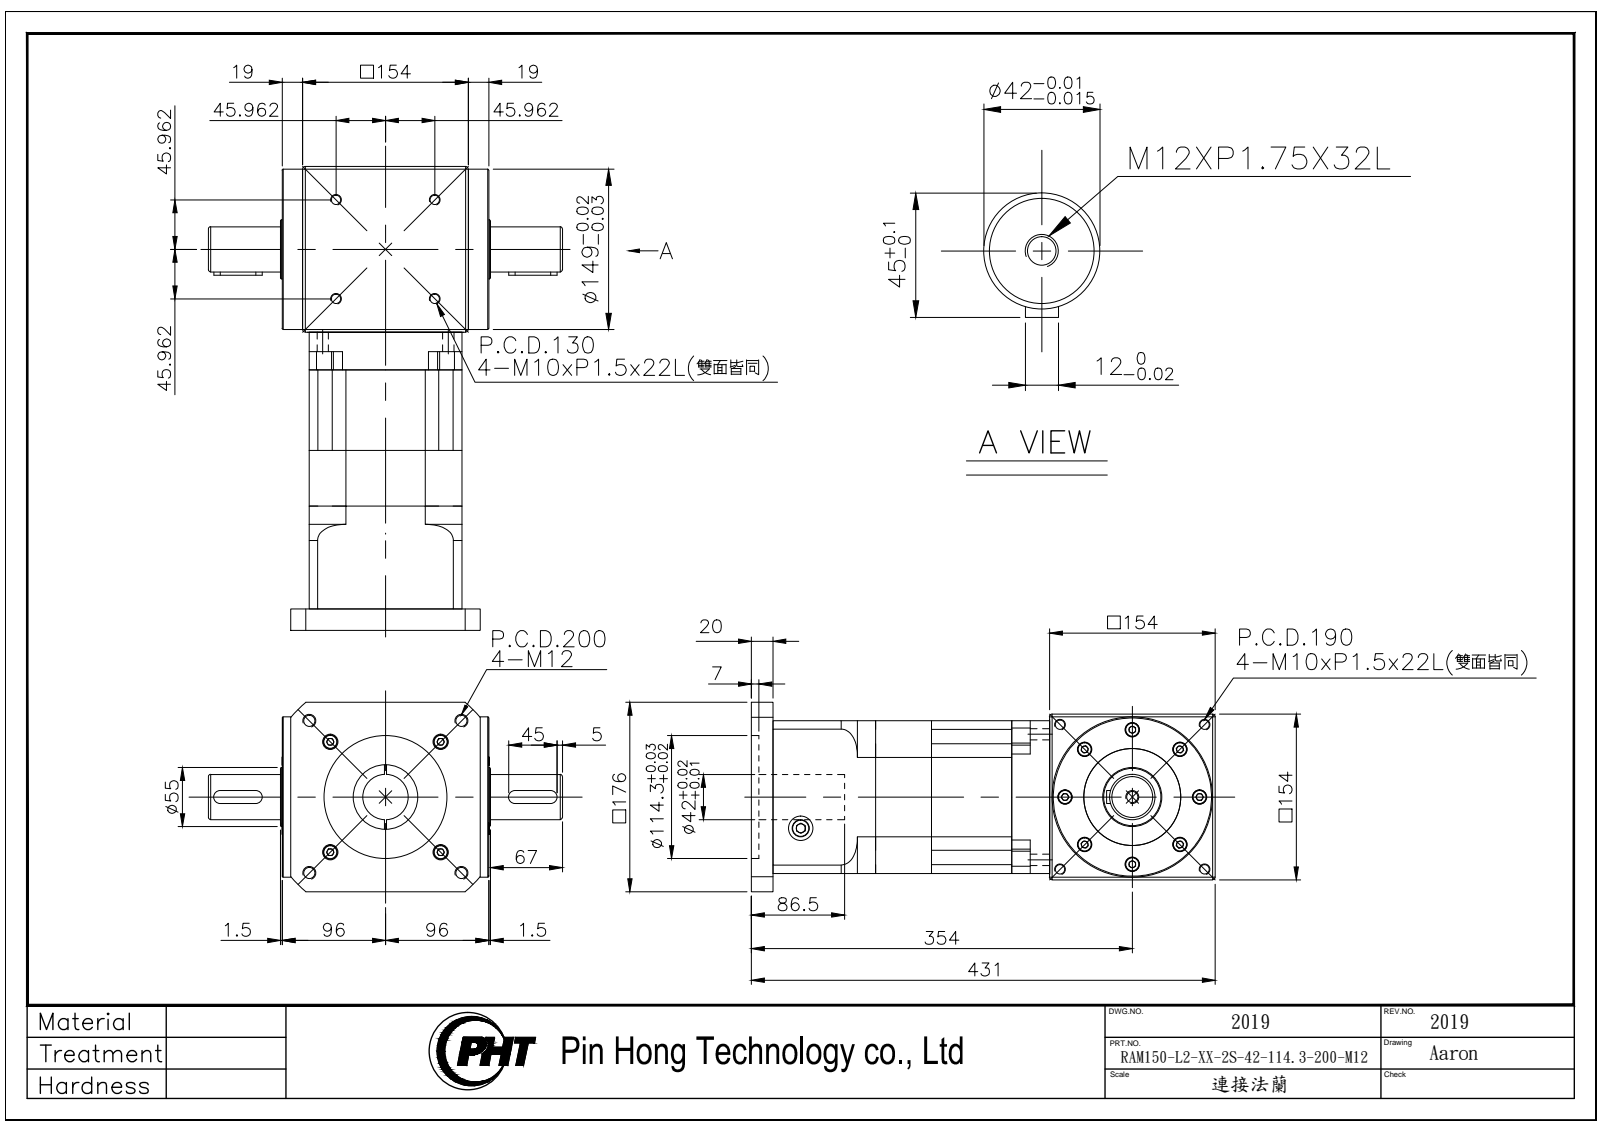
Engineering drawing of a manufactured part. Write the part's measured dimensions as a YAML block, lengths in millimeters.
part_name: "RAM150-L2-XX-2S-42-114.3-200-M12_2019"
step_written_by: "SolidWorks 2016 (AUTOMOTIVE_DESIGN)"
units: millimeters
bodies: {solids: 7, faces: 920, planar: 428, cylindrical: 328, other: 164}
overall_size: [431, 329, 176]
volume: 9426000
surface_area: 649264
round_holes:
  - {diameter: 8.5, count: 12}
  - {diameter: 9, count: 12}
  - {diameter: 14, count: 12}
  - {diameter: 11, count: 8}
  - {diameter: 17.5, count: 8}
  - {diameter: 10.2, count: 5}
  - {diameter: 6.8, count: 4}
  - {diameter: 10.5, count: 4}
  - {diameter: 22.5, count: 2}
  - {diameter: 4.08, count: 1}
  - {diameter: 42, count: 1}
  - {diameter: 60, count: 1}
round_bosses_or_shafts:
  - {diameter: 16, count: 12}
  - {diameter: 13, count: 4}
  - {diameter: 149, count: 1}
  - {diameter: 130, count: 1}
  - {diameter: 90, count: 1}
  - {diameter: 74, count: 1}
  - {diameter: 55, count: 1}
  - {diameter: 42, count: 1}
partial_cylinders:
  - {radius: 6, count: 4}
  - {radius: 10, count: 4}
  - {radius: 80, count: 1}
  - {radius: 95, count: 1}
  - {radius: 107.4, count: 1}
  - {radius: 115, count: 1}
face_to_face_distances: [6, 148, 154, 142, 51.8, 126.5, 74.7, 161.5, 109.7, 35]
hole_center_spacings: [71, 18.72, 18.79, 23.06, 36.4, 47.83, 67.34, 82.93]
